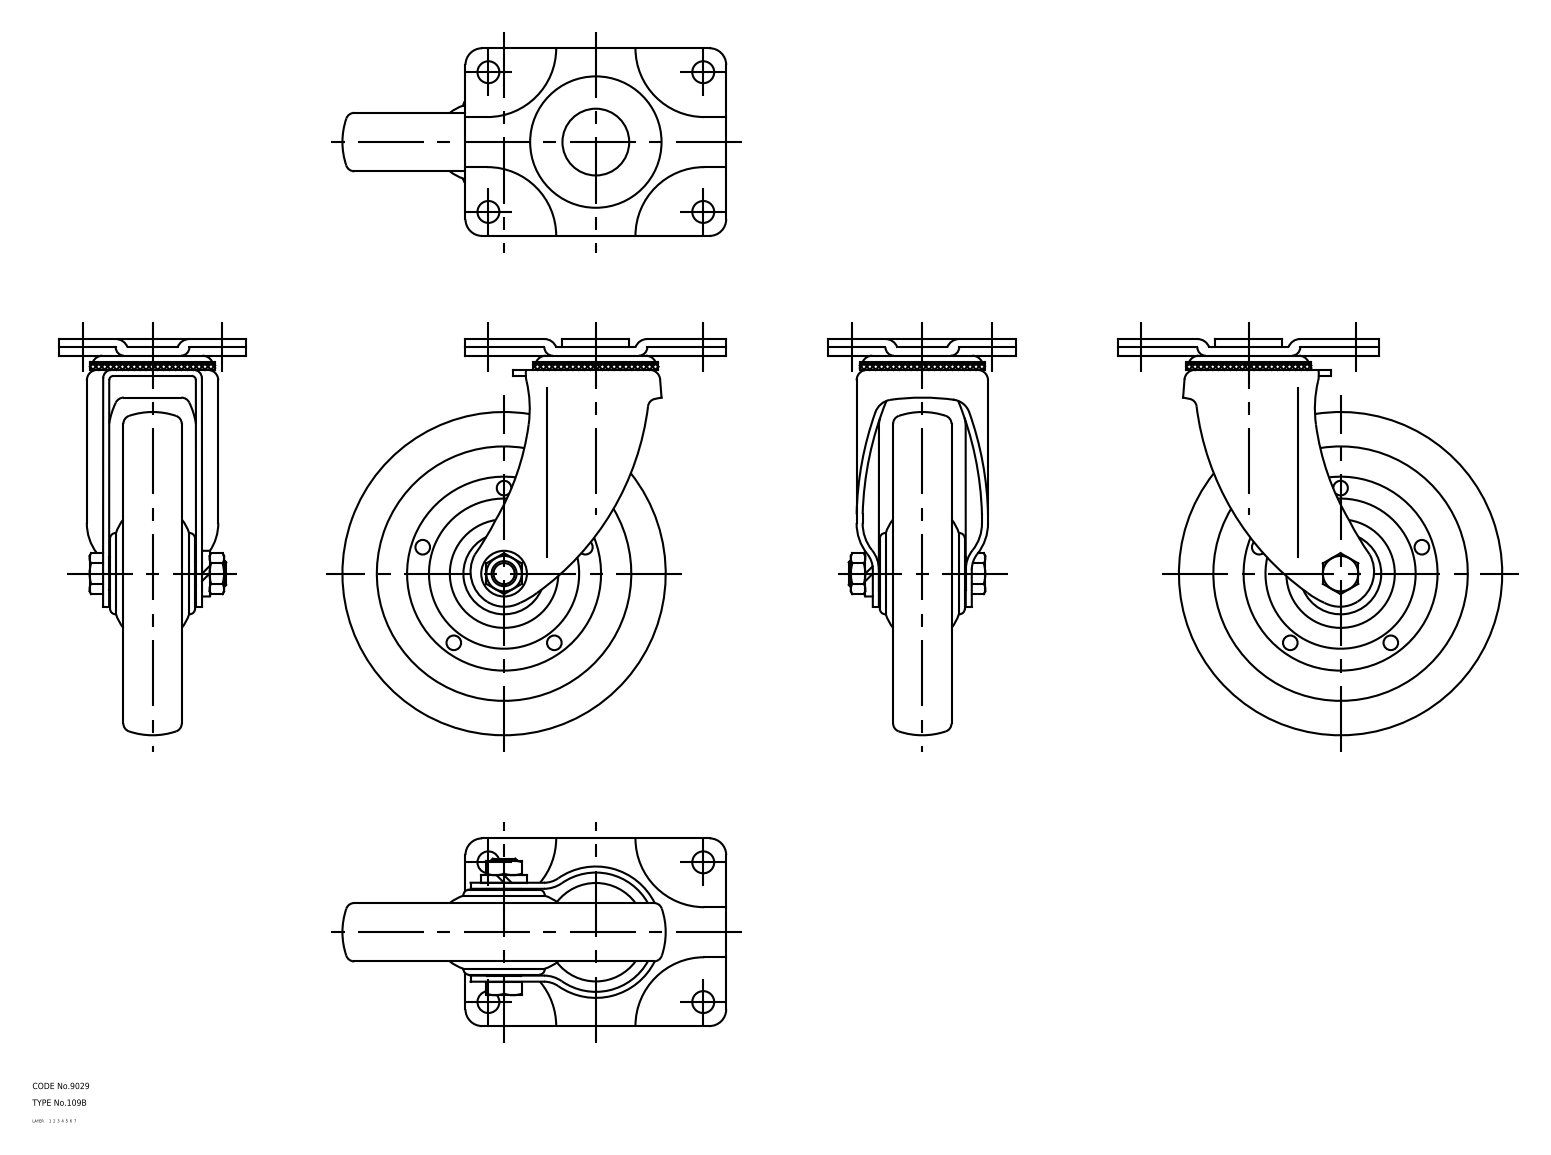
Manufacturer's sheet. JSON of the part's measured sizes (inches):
{"part_name": "67125578; 67125591; 67125604; 67125617 (+1 more)", "step_written_by": "CADfix (AUTOMOTIVE_DESIGN)", "units": "inches", "bodies": {"solids": 5, "faces": 265, "planar": 0, "cylindrical": 0, "other": 265}, "overall_size": [7.48, 7.244, 3.543], "volume_in3": 34.59, "surface_area_in2": 184.3}
